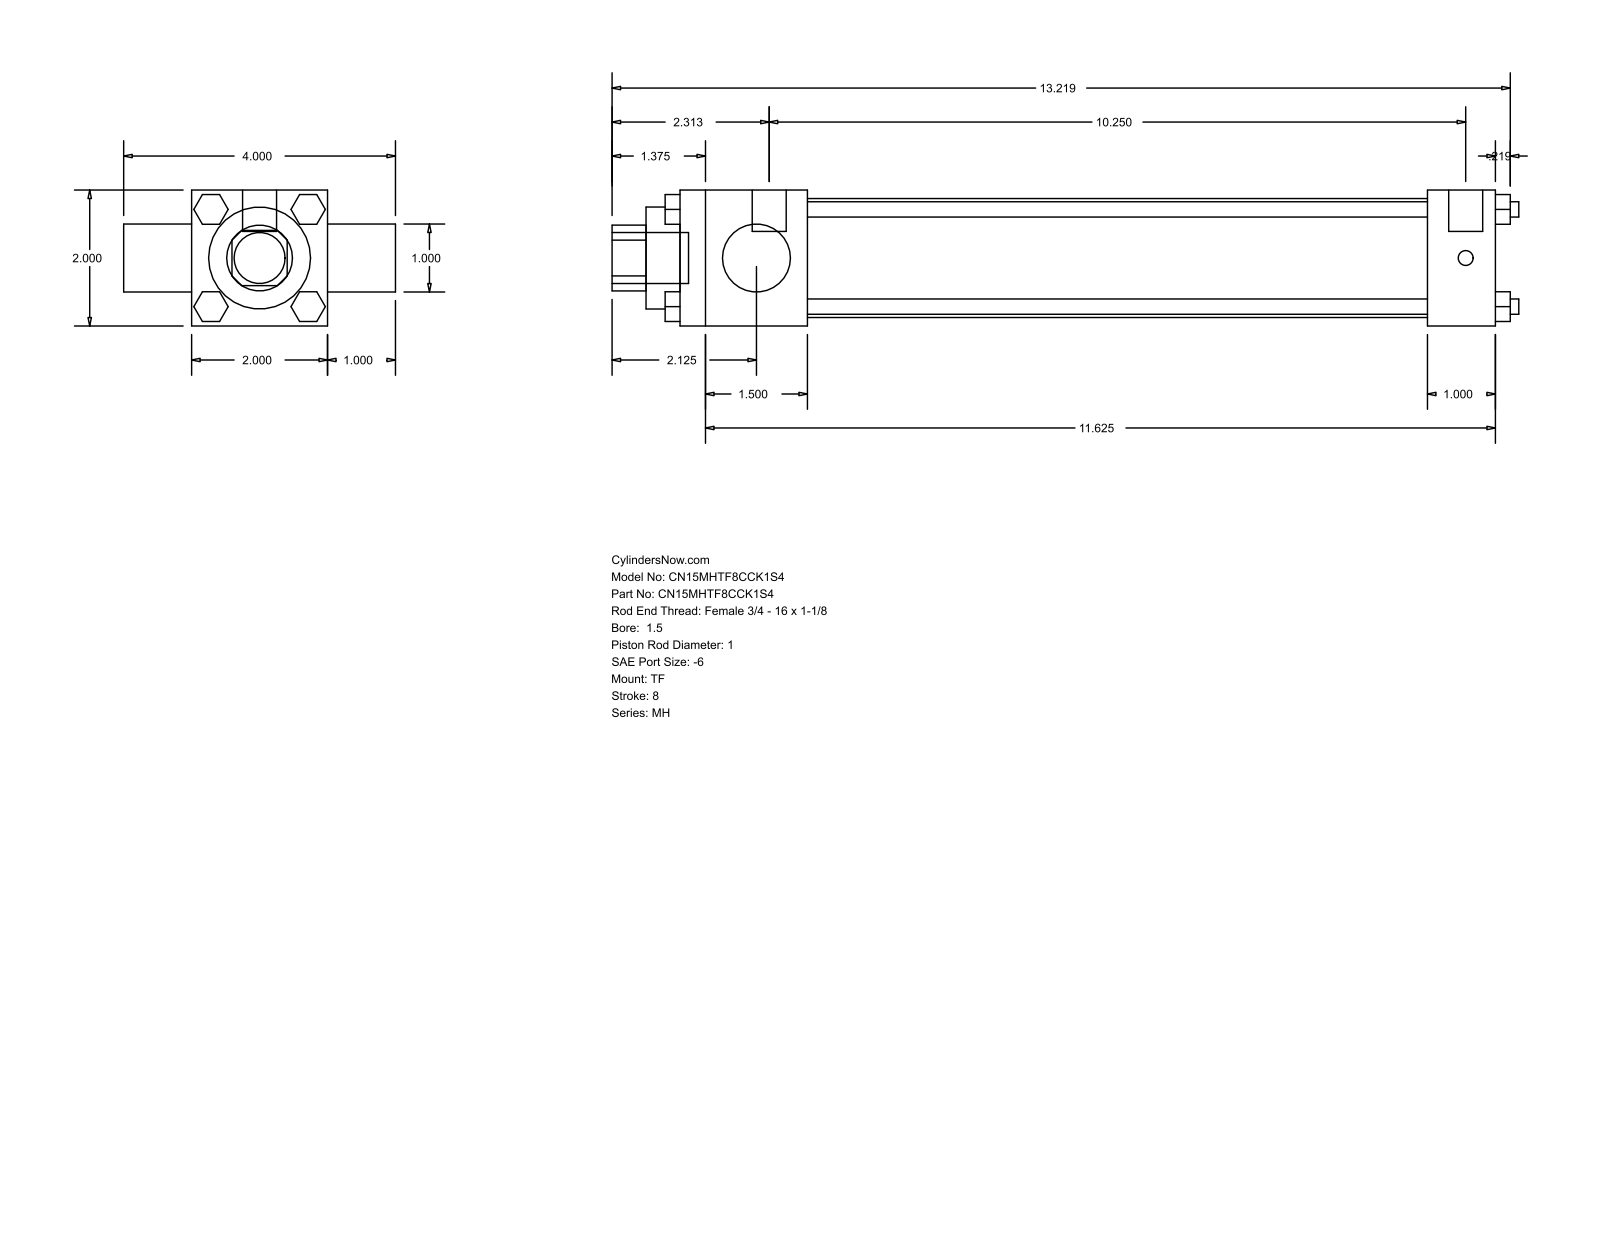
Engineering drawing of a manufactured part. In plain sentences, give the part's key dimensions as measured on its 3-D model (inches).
The part is named "MH_TF__0150_1". Its 3-D file was written by "GSSL Pune (CONFIG_CONTROL_DESIGN)". It is 0 solids with 120 faces: 92 planar, 28 cylindrical and 0 other. Overall it measures 13.344 by 4 by 2 inches. Round holes: 2 of diameter 1, 1 of diameter 1.5, 1 of diameter 1.75. Round bosses or shafts: 4 of diameter 0.225, 3 of diameter 0.219, 2 of diameter 0.5, 1 of diameter 0.75. Partial cylindrical surfaces (rounded edges, fillets, slot ends): 1 of radius 0.484. The main face-to-face distances are 2, 1, 12, 3, 1.875, 10.125, 11, 9.125, 12.219, 0.5.
